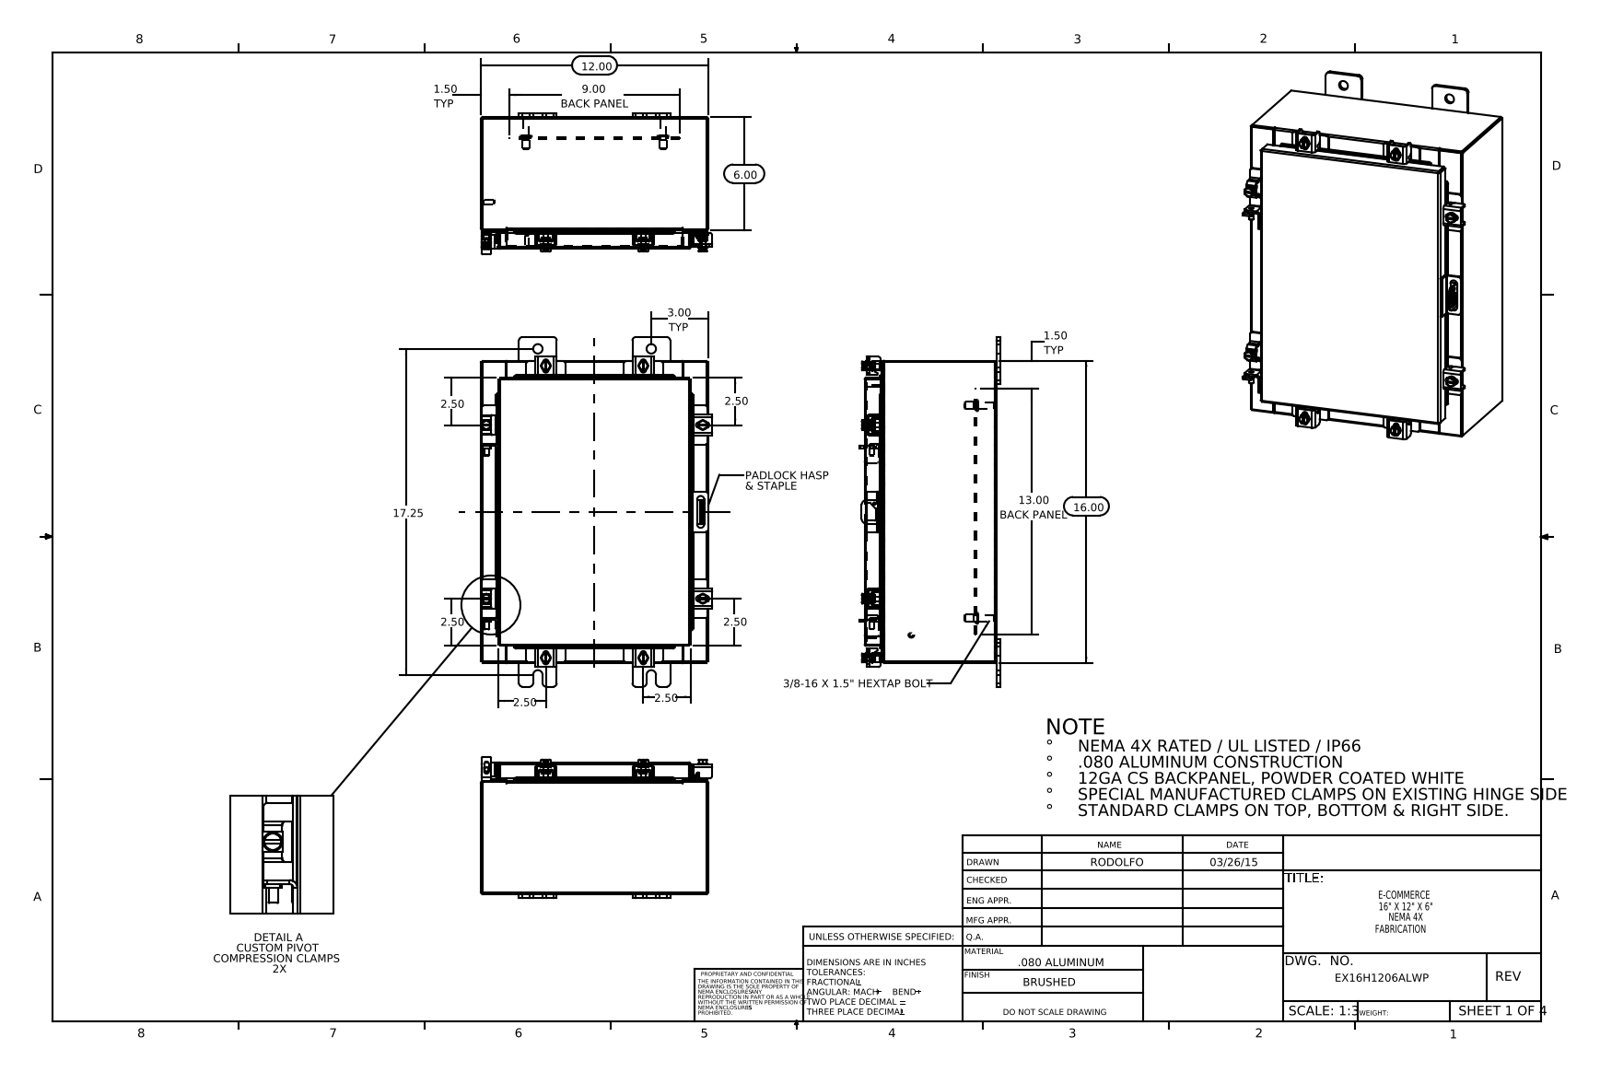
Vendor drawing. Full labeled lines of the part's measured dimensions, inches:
Part name (STEP PRODUCT): 22104005_DEFAULT_RTP30; EX16H1206ALWP; EX16H1206ALWP Clamp Assembly; EX16H1206ALWP Bottom (+8 more)
STEP written by: SolidWorks 2014 (CONFIG_CONTROL_DESIGN)
Units: inches
Bodies: 59 solids, 1468 faces (791 planar, 549 cylindrical, 128 other)
Overall size (bounding box): 18.5 × 12.211 × 7.453
Volume: 81.47 in³ · Surface area: 2 053 in²
Round holes (diameter × count): ⌀0.213 ×8, ⌀0.26 ×8, ⌀0.5 ×8, ⌀0.125 ×1, ⌀0.25 ×1
Round bosses / shafts (diameter × count): ⌀0.5 ×8, ⌀0.25 ×8, ⌀0.399 ×6, ⌀0.625 ×4, ⌀0.375 ×4, ⌀0.33 ×4, ⌀0.315 ×2, ⌀0.236 ×2
Partial cylindrical surfaces — rounded edges, fillets, slot ends (radius × count): R0.06 ×34, R0.19 ×24, R0.013 ×22, R0.088 ×22, R0.1 ×16, R0.09 ×14, R0.12 ×14, R0.141 ×12
Main face-to-face distances: 0.075, 6.9, 11.925, 6.975, 6.826, 15.925, 5.925, 0.975, 1, 1.075
Hole centre spacings: 2.347, 4.44, 8.874, 10.433, 12.715, 13.392, 13.852, 14.857
